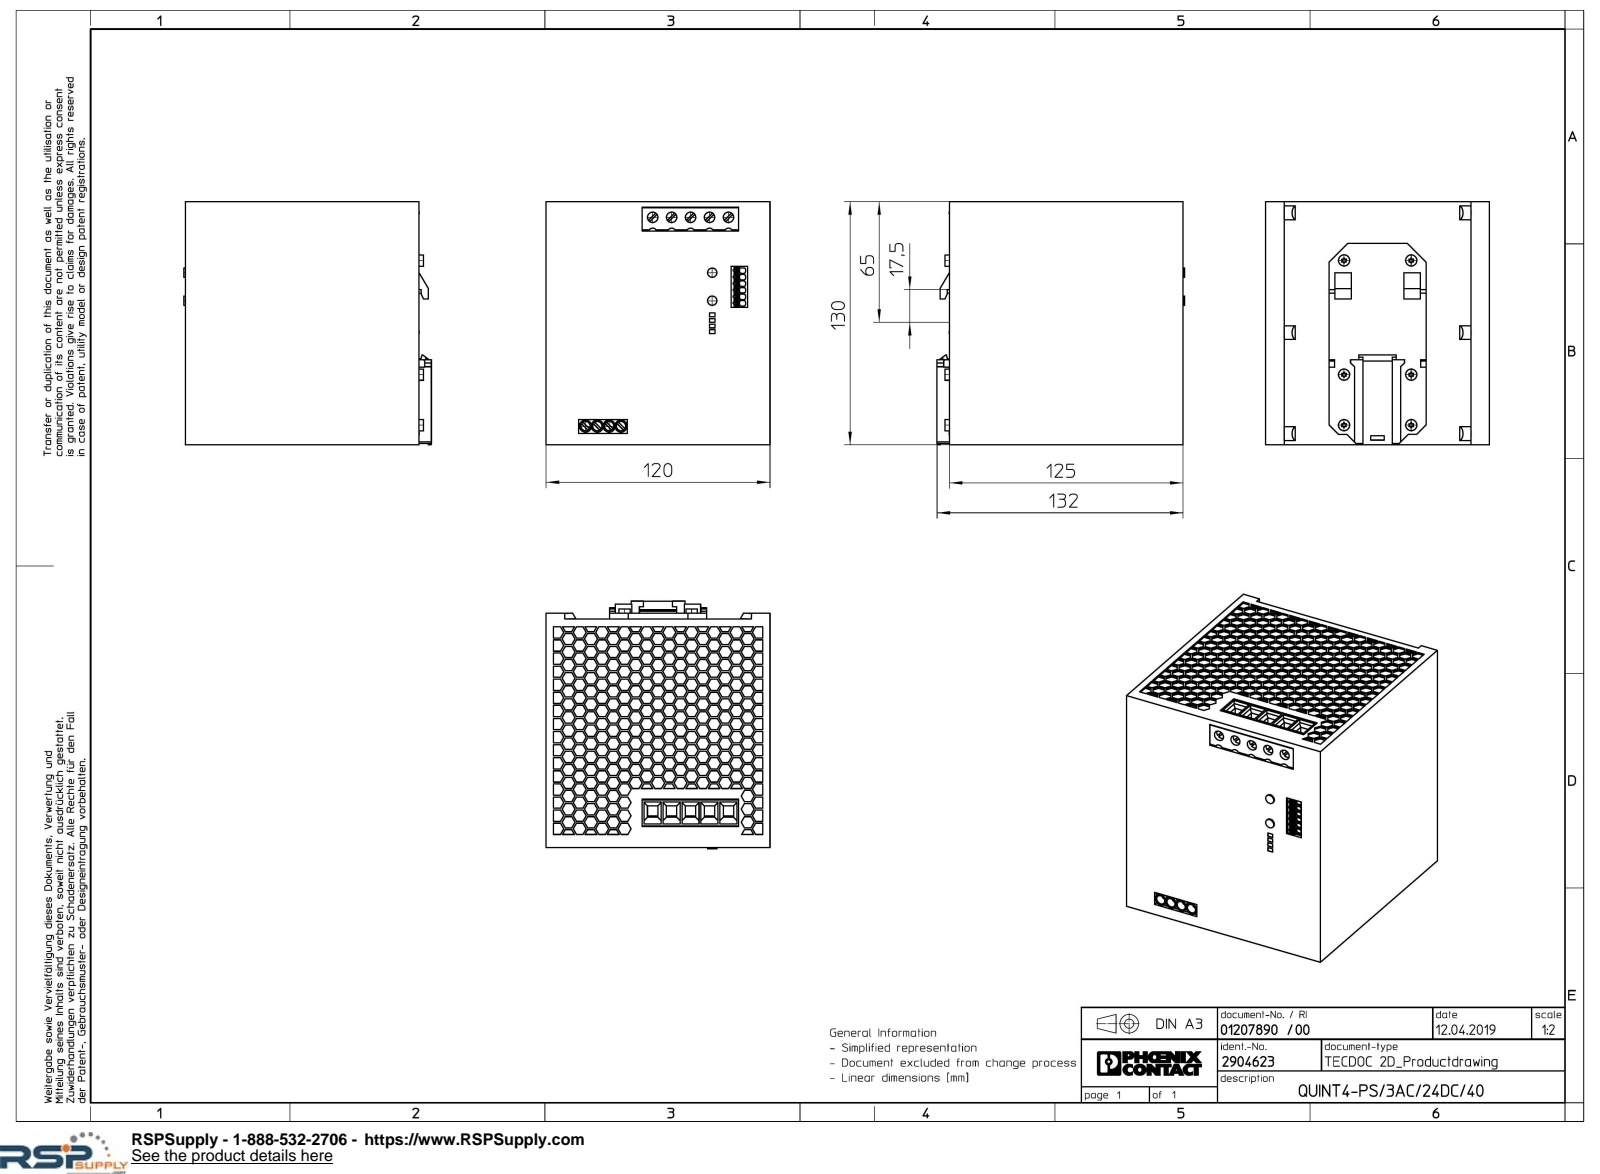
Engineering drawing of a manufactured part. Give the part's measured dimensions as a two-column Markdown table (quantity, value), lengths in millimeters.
| quantity | value |
| --- | --- |
| part name | QUINT4_PS_3AC_24DC_40-select |
| STEP written by | Creo Elements/Direct Modeling 20.1A 29-Sep-2018 (C) Parametric Technology GmbH (AUTOMOTIVE_DESIGN) |
| units | millimeters |
| bodies | 1 solid, 4604 faces (4441 planar, 151 cylindrical, 12 other) |
| overall size | 132.55 × 130 × 120 |
| volume | 1 920 000 mm³ |
| surface area | 112 852 mm² |
| round holes (diameter × count) | 5.6 × 5, 5 × 4, 6.11 × 1 |
| round bosses / shafts (diameter × count) | 6 × 6, 5 × 2 |
| partial cylindrical surfaces (radius × count) | 0.1 × 72, 0.97 × 12, 0.57 × 6, 0.6 × 6, 2.3 × 5, 3.25 × 4, 3.75 × 2, 3.75 × 2 |
| main face-to-face distances | 120, 0.8, 129.2, 128.4, 122.25, 3, 125.25, 130, 6.5, 9.5 |
| hole center spacings | 10.16, 6.35, 20.32, 12.7, 30.48, 19.05, 40.64 |
